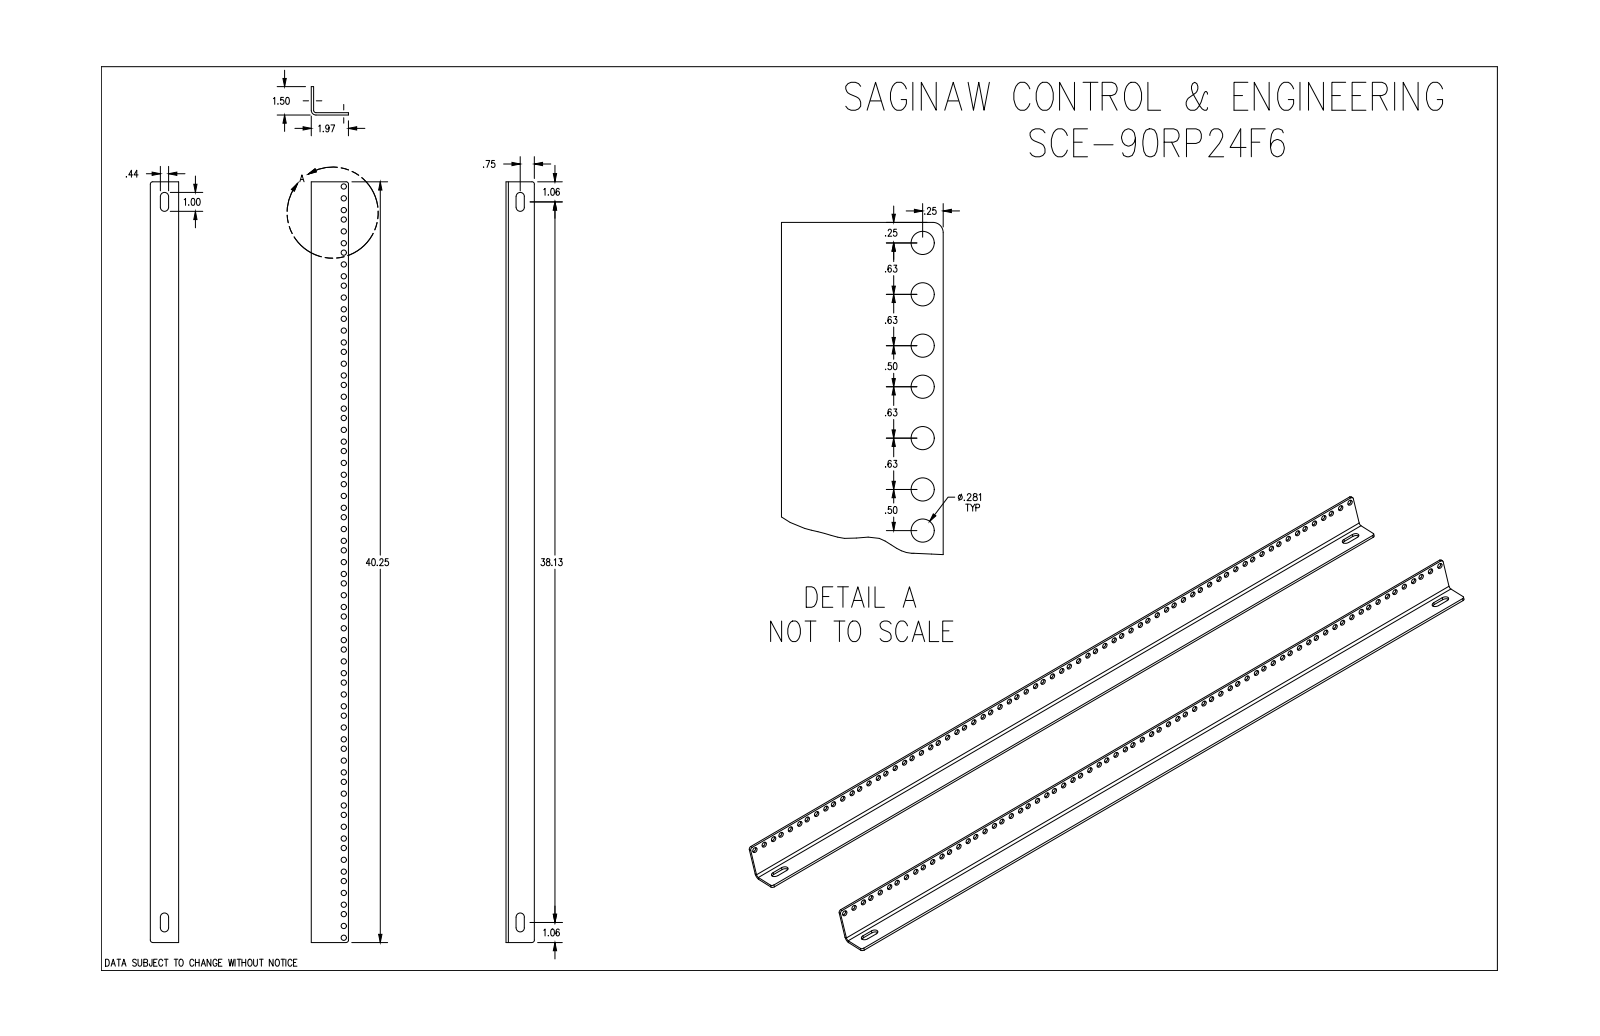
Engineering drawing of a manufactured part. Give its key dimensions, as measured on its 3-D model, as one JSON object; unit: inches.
{"part_name": "SCE-90RP24F6", "step_written_by": "SolidWorks 2019 (AUTOMOTIVE_DESIGN)", "units": "inches", "bodies": {"solids": 1, "faces": 164, "planar": 16, "cylindrical": 148, "other": 0}, "overall_size": [40.25, 1.969, 1.5], "volume_in3": 15.78, "surface_area_in2": 271.6, "round_holes": [[0.281, 69]], "partial_cylinders_radius": [[0.219, 4], [0.13, 3], [0.125, 2], [0.25, 1]], "face_to_face_distances": [0.125, 1.844, 1.969, 1.5, 1.375, 40.25, 0.531, 0.969, 0.407, 0.844], "hole_center_spacings": [1.75, 3.5, 5.25, 7, 8.75, 0.625, 0.625, 1.25]}
